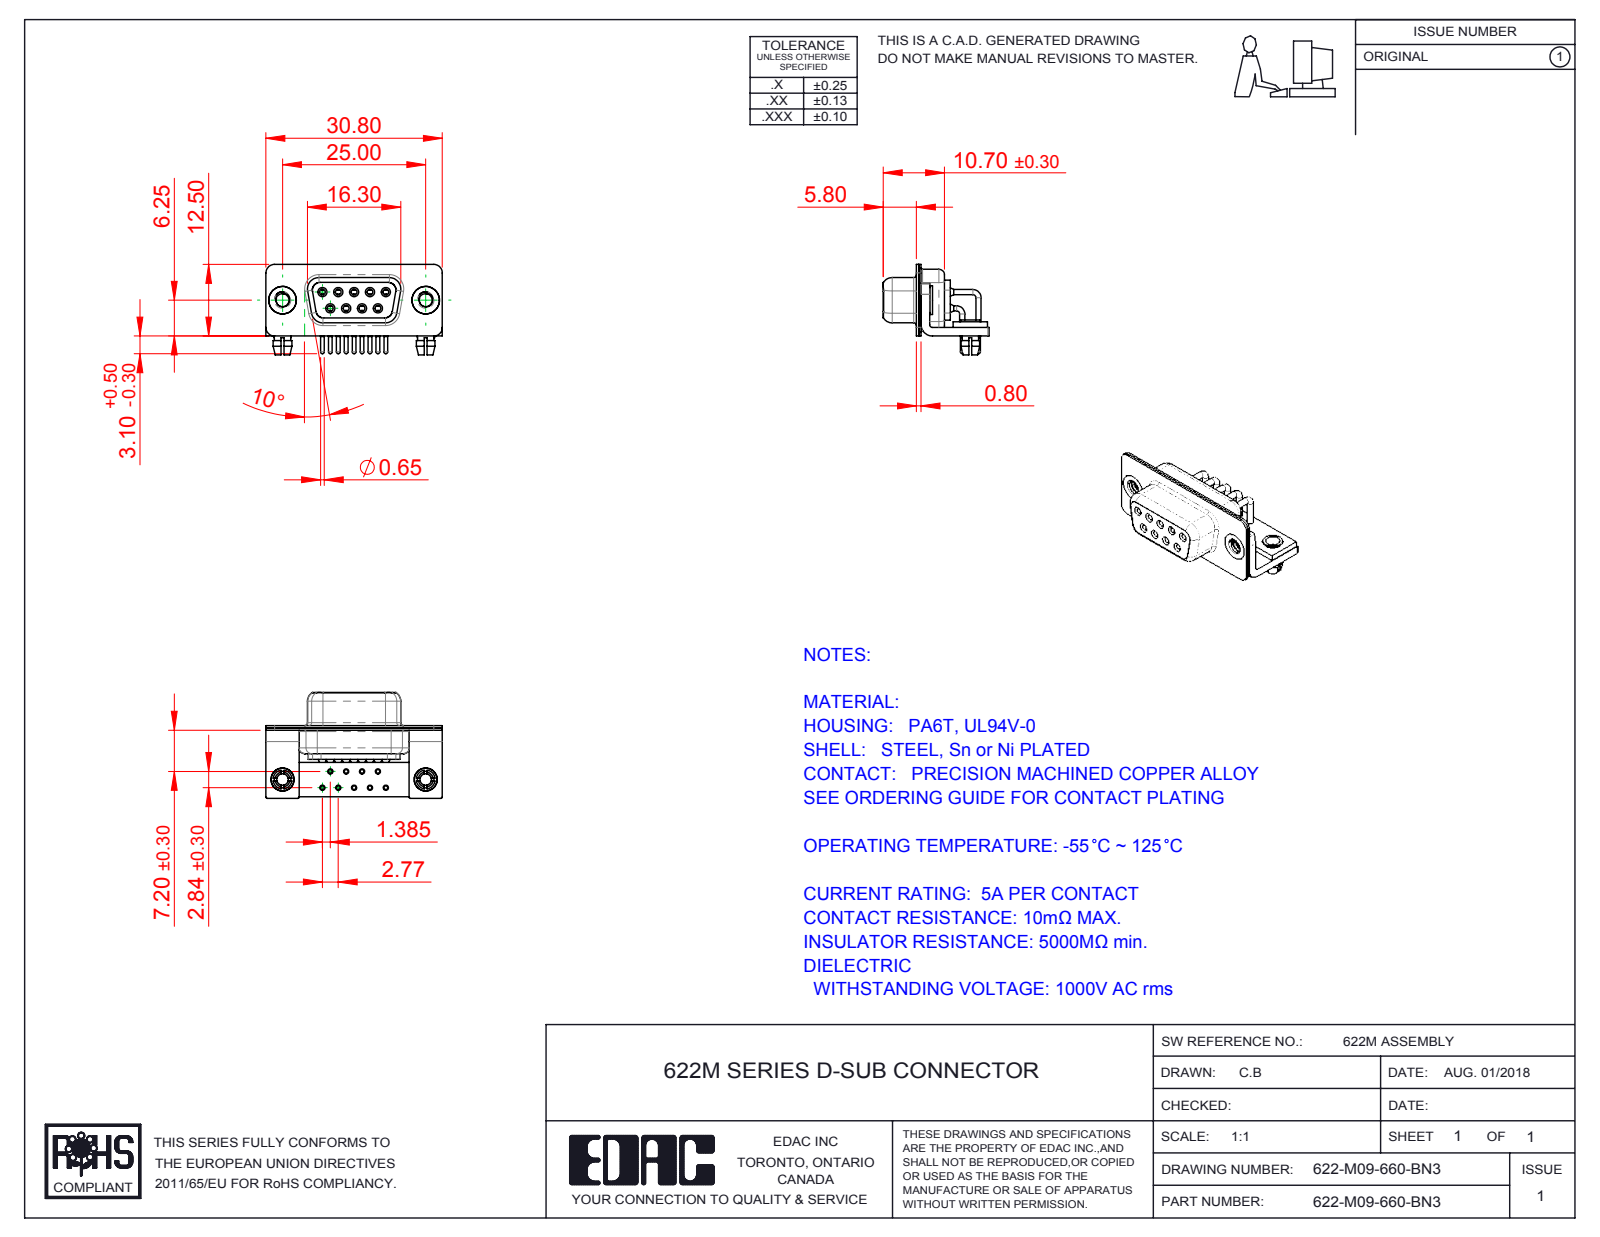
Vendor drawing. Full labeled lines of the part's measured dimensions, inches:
Part name (STEP PRODUCT): 622M Stabilizer Board_09 Contacts; 622M Stabilizer Bracket; 622-M09-660-BN3; 622M 4-40 Threaded Rivet_Stabilizer (+6 more)
STEP written by: SolidWorks 2016 (CONFIG_CONTROL_DESIGN)
Units: inches
Bodies: 19 solids, 916 faces (276 planar, 416 cylindrical, 224 other)
Overall size (bounding box): 1.213 × 0.728 × 0.622
Volume: 0.133 in³ · Surface area: 8.933 in²
Round holes (diameter × count): ⌀0.079 ×11, ⌀0.035 ×9, ⌀0.039 ×9, ⌀0.043 ×9, ⌀0.067 ×9, ⌀0.071 ×9, ⌀0.089 ×2, ⌀0.098 ×2, ⌀0.126 ×2, ⌀0.157 ×2, ⌀0.189 ×2
Round bosses / shafts (diameter × count): ⌀0.063 ×9, ⌀0.059 ×9, ⌀0.035 ×9, ⌀0.026 ×9, ⌀0.197 ×2, ⌀0.193 ×2, ⌀0.157 ×2, ⌀0.134 ×2
Partial cylindrical surfaces — rounded edges, fillets, slot ends (radius × count): R0.01 ×16, R0.059 ×16, R0.079 ×13, R0.053 ×8, R0.063 ×8, R0.02 ×5, R0.024 ×4, R0.026 ×4
Main face-to-face distances: 0.016, 0.031, 0.059, 0.091, 0.075, 0.039, 0.368, 0.057, 0.352, 0.033
Hole centre spacings: 0.124, 0.109, 0.218, 0.198, 0.198, 0.327, 0.294, 0.295
